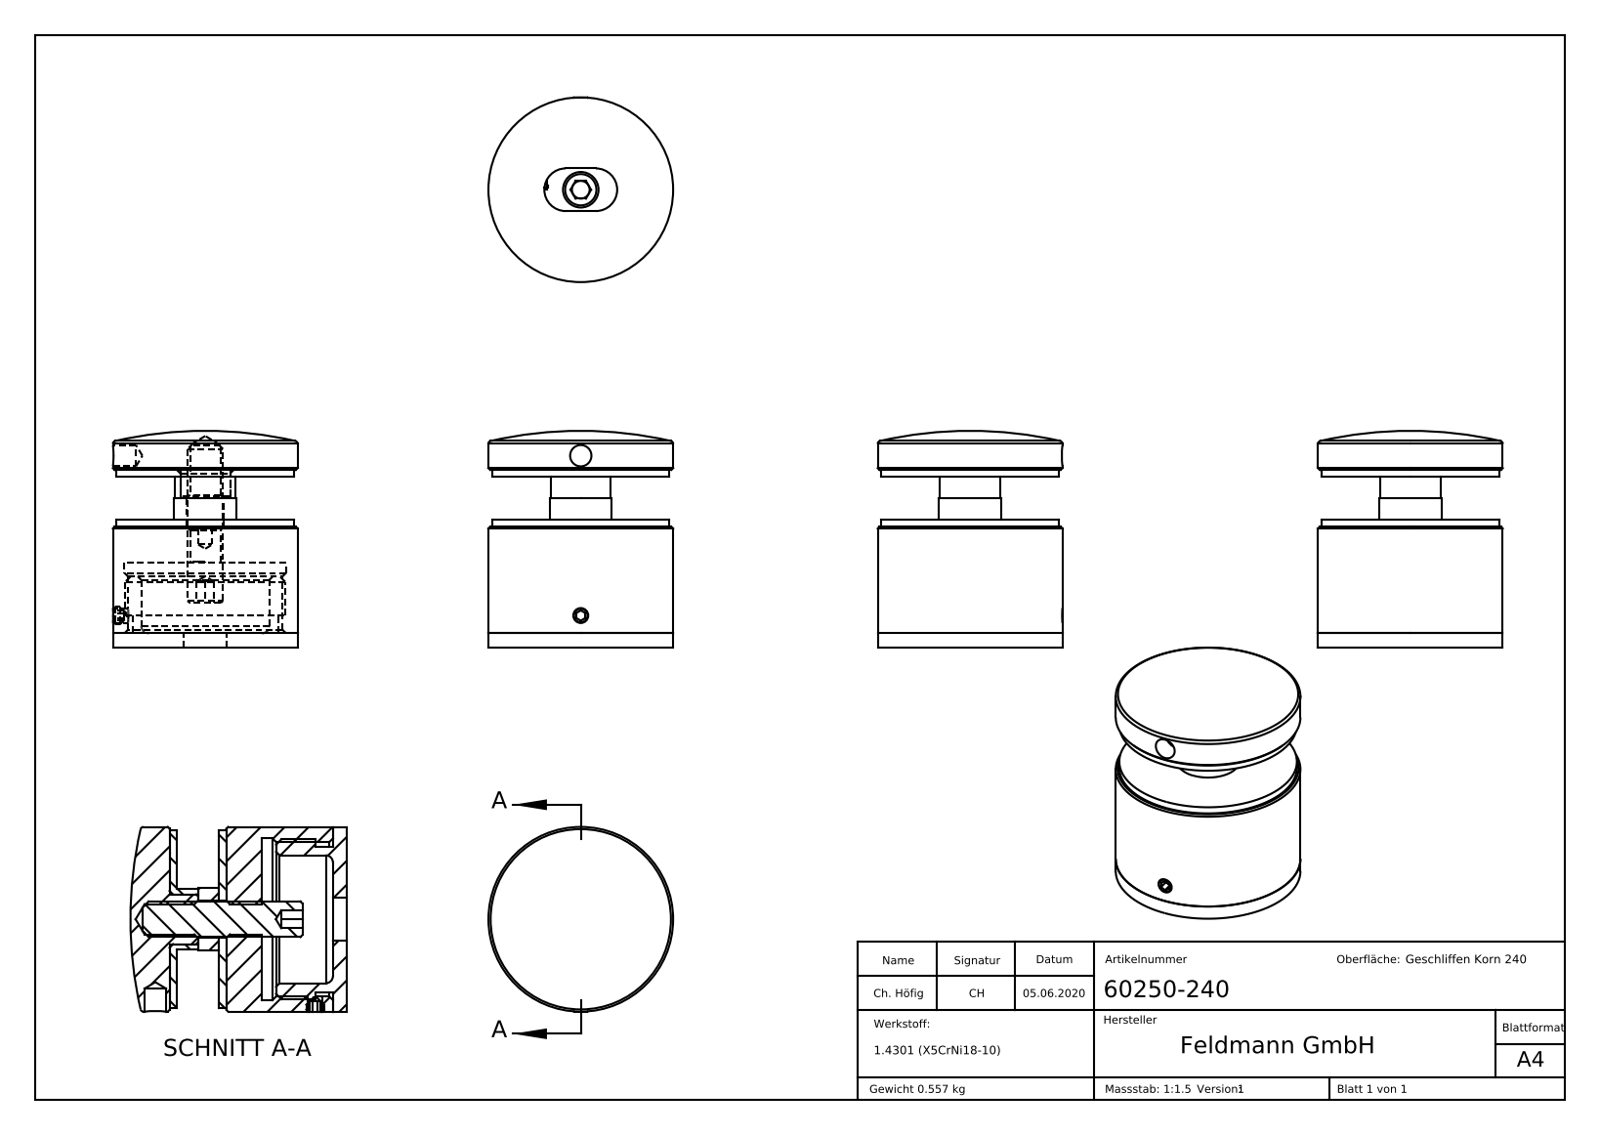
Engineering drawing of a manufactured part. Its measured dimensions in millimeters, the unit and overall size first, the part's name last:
Units: millimetres
Overall size (bounding box): 120.56 × 70 × 52
Round holes (diameter × count): ⌀4 ×2, ⌀4.2 ×1, ⌀6 ×1, ⌀8.5 ×1, ⌀10.5 ×1, ⌀14 ×1, ⌀36 ×1, ⌀43.5 ×1, ⌀45.5 ×1
Round bosses / shafts (diameter × count): ⌀52 ×1, ⌀50 ×1, ⌀45 ×1, ⌀41 ×1, ⌀17.5 ×1, ⌀17 ×1, ⌀10 ×1, ⌀5 ×1
Partial cylindrical surfaces — rounded edges, fillets, slot ends (radius × count): R6 ×2
Main face-to-face distances: 16, 14, 2, 12, 24, 4, 30, 34, 36, 50
Hole centre spacings: 16.5, 33, 45
Volume: 80 320 mm³ · Surface area: 38 870 mm²
Bodies: 8 solids, 371 faces (192 planar, 26 cylindrical, 153 other)
Part name (STEP PRODUCT): 60250-XXX Teil6_60250-XXX Teil6; DIN913; 60250-XXX Teil5_60250-XXX Teil5; 60250-XXX Teil1 (+8 more)
STEP written by: SolidWorks 2015 (CONFIG_CONTROL_DESIGN)
